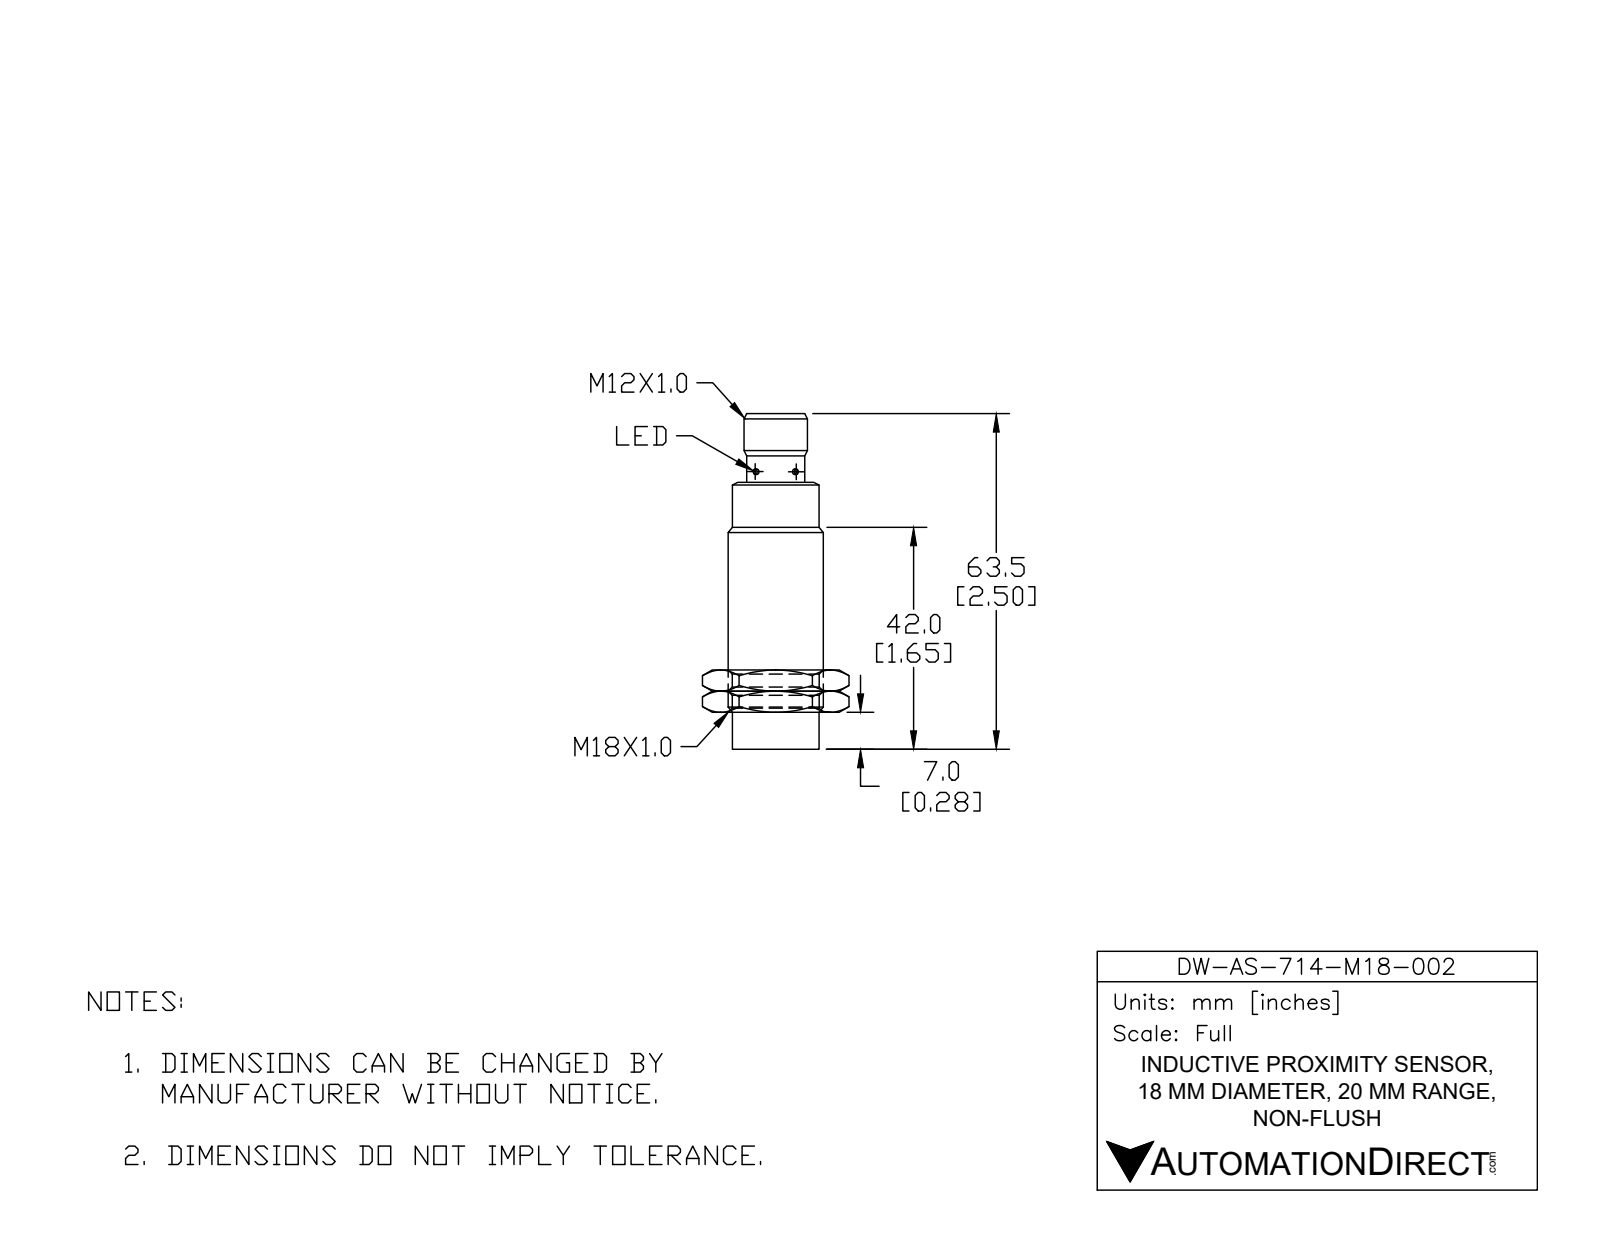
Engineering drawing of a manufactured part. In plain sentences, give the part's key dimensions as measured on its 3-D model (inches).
The part is named "DW-AS-714-M18-002". Its 3-D file was written by "SolidWorks 2017 (AUTOMOTIVE_DESIGN)". It is 1 solid with 40 faces: 8 planar, 17 cylindrical and 15 other. Overall it measures 2.5 by 0.709 by 0.709 inches. Its volume is 0.778 cubic inches and its surface area 6.608 square inches. Round holes: 2 of diameter 0.118, 1 of diameter 0.335. Round bosses or shafts: 4 of diameter 0.04, 1 of diameter 0.709, 1 of diameter 0.646, 1 of diameter 0.459, 1 of diameter 0.415. Partial cylindrical surfaces (rounded edges, fillets, slot ends): 2 of radius 0.02. The main face-to-face distances are 2.157, 1.988, 0.169, 2.5, 0.512, 0.343, 0.276, 1.713, 1.882, 2.224.
